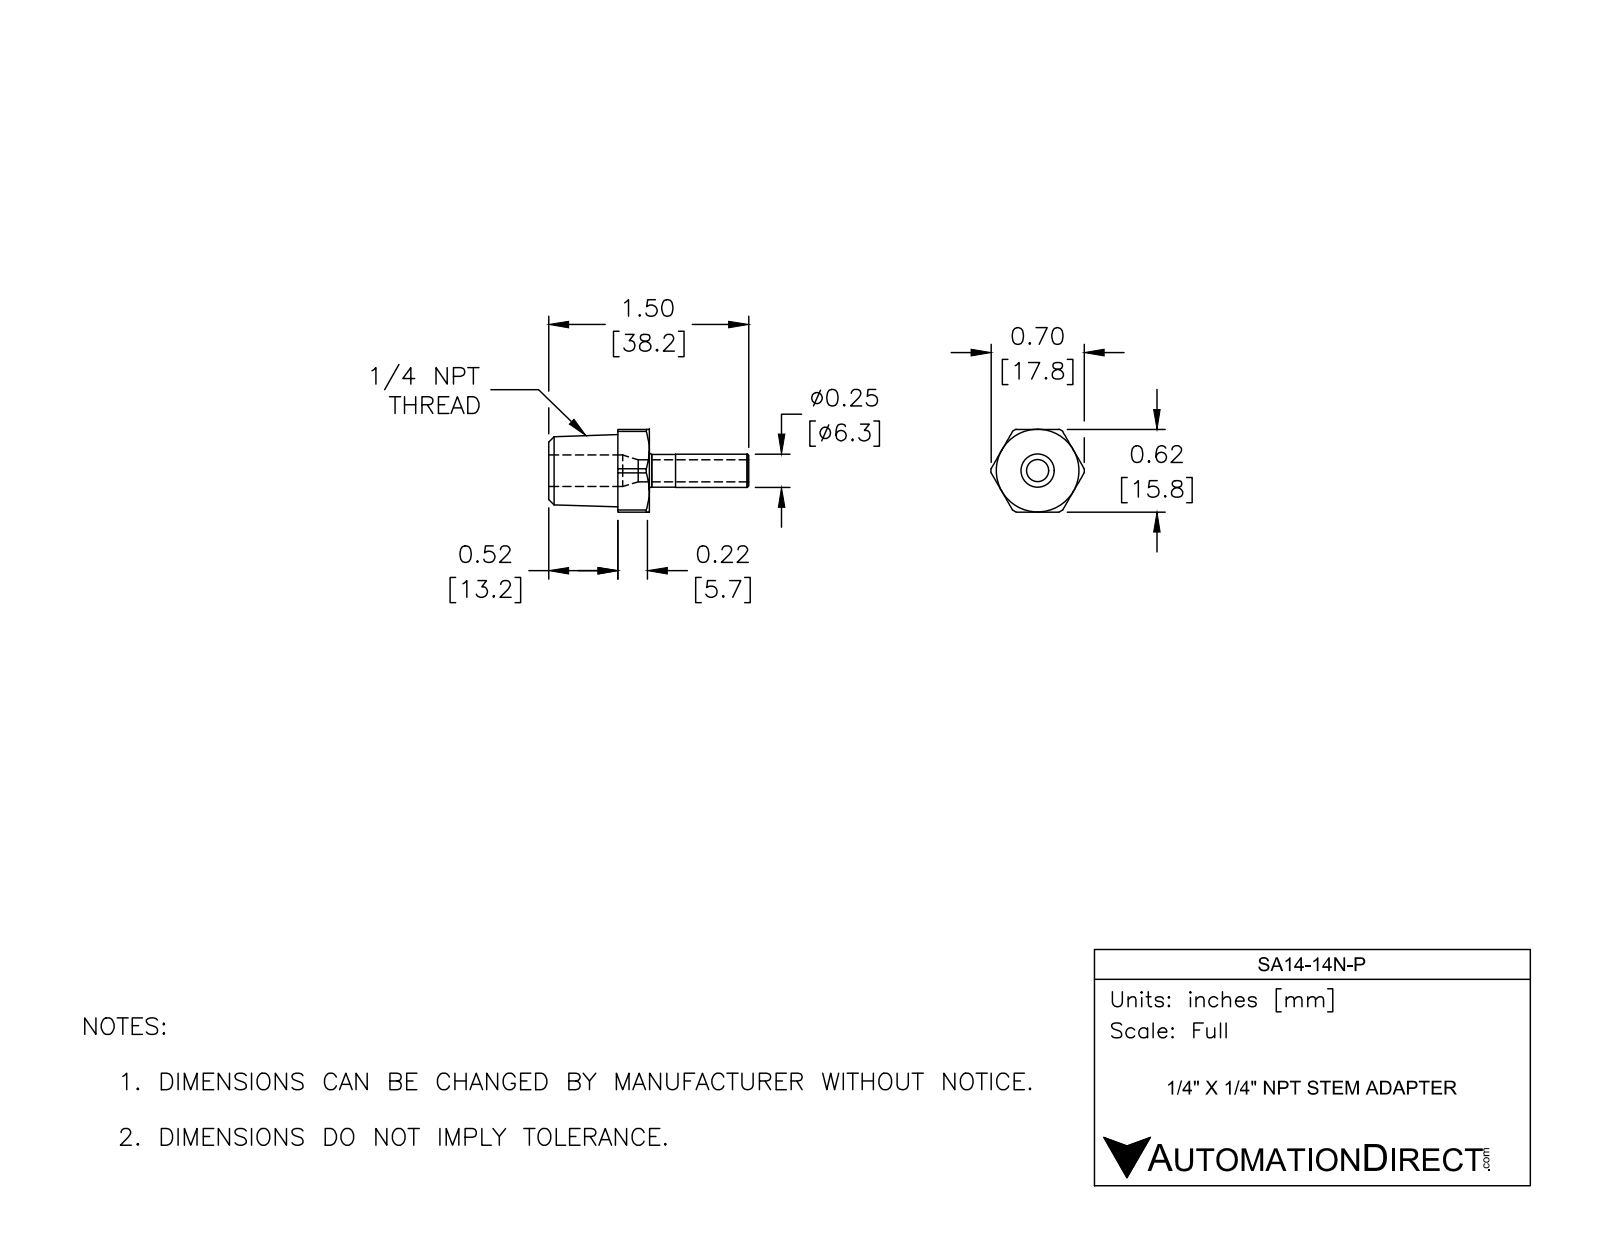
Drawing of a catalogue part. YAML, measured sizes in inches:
part_name: "SA14-14N-P"
step_written_by: "SolidWorks 2017 (AUTOMOTIVE_DESIGN)"
units: inches
bodies: {solids: 1, faces: 43, planar: 11, cylindrical: 15, other: 17}
overall_size: [1.504, 0.701, 0.622]
volume: 0.181
surface_area: 3.386
round_holes:
  - {diameter: 0.165, count: 1}
  - {diameter: 0.236, count: 1}
round_bosses_or_shafts:
  - {diameter: 0.25, count: 1}
  - {diameter: 0.246, count: 1}
partial_cylinders:
  - {radius: 0.35, count: 1}
face_to_face_distances: [0.622, 0.756, 0.52, 0.236, 1.504, 0.984, 0.748, 0.953, 0.433, 0.197]
